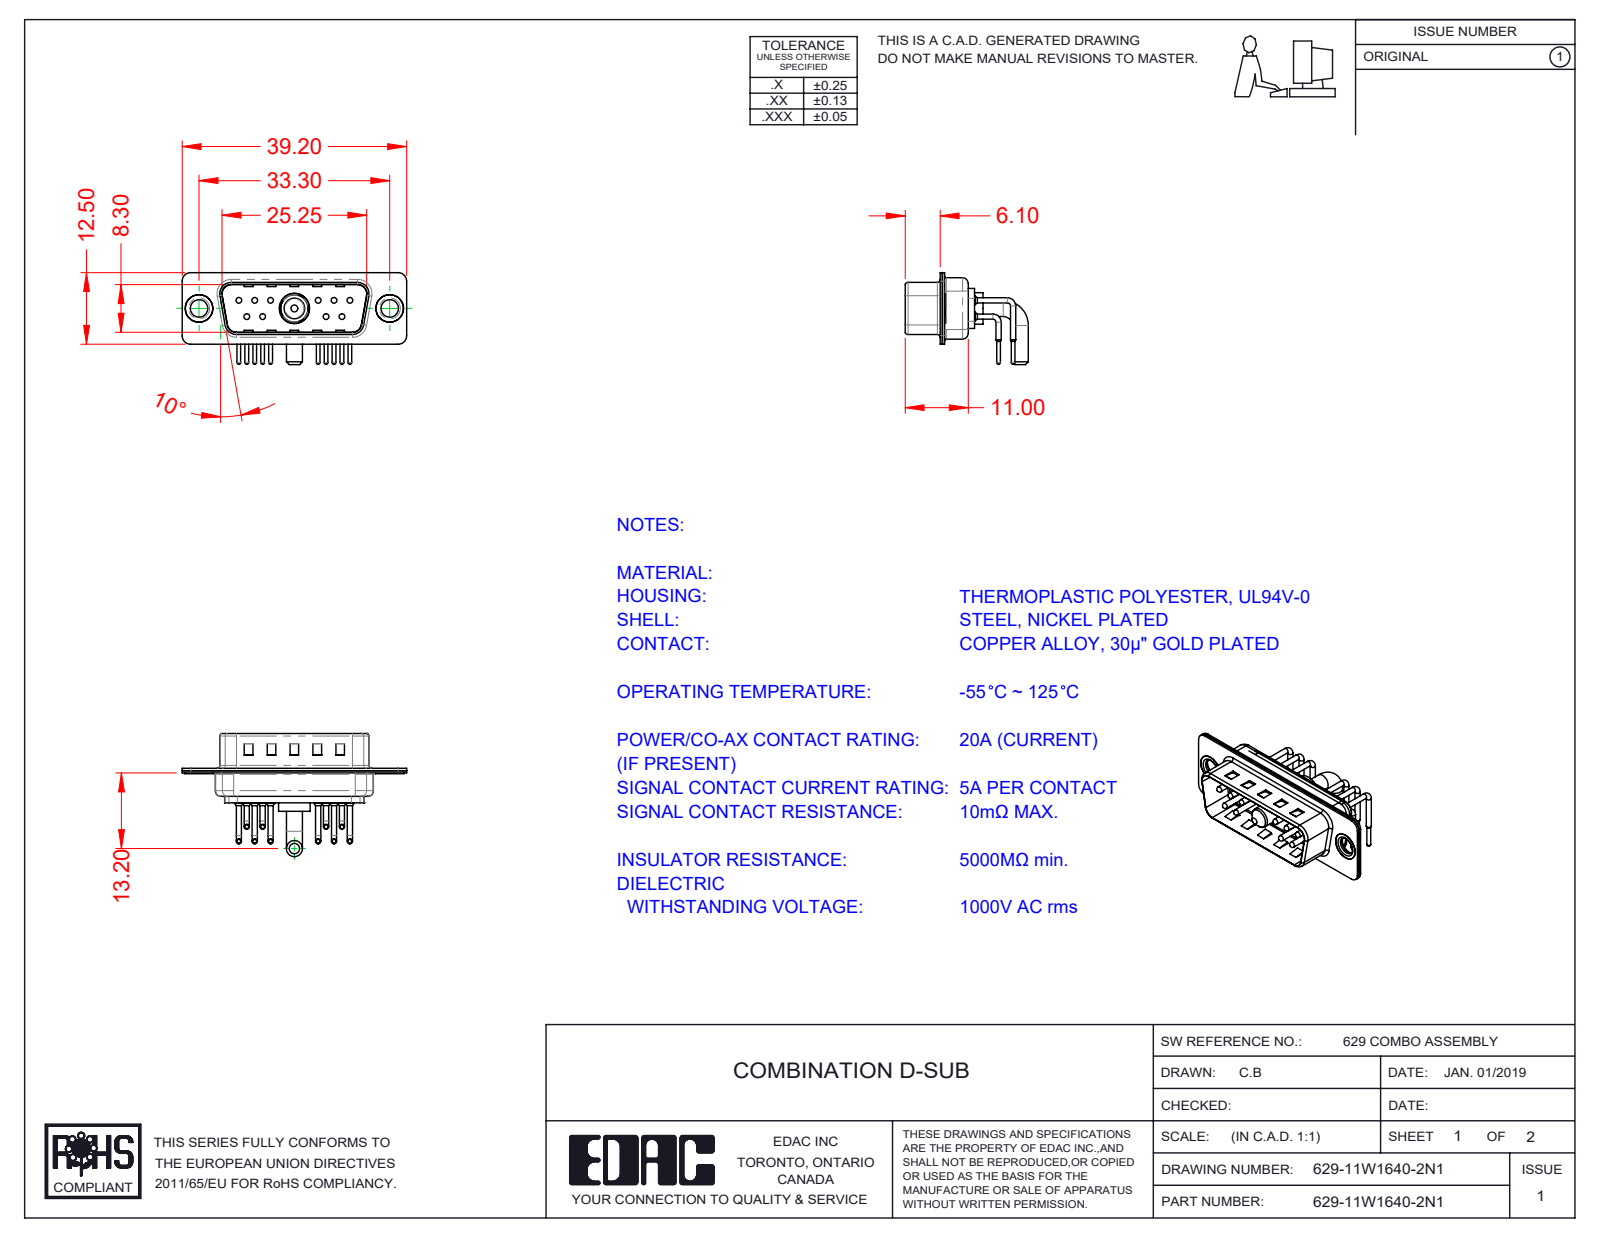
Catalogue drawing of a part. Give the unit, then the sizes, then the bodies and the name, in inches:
Units: inches
Overall size (bounding box): 1.543 × 0.846 × 0.632
Round holes (diameter × count): ⌀0.03 ×10, ⌀0.063 ×10, ⌀0.079 ×10, ⌀0.12 ×2, ⌀0.157 ×2, ⌀0.189 ×2, ⌀0.191 ×1, ⌀0.209 ×1
Round bosses / shafts (diameter × count): ⌀0.035 ×20, ⌀0.059 ×10, ⌀0.039 ×10, ⌀0.026 ×10, ⌀0.197 ×2, ⌀0.193 ×2, ⌀0.14 ×2, ⌀0.11 ×2
Partial cylindrical surfaces — rounded edges, fillets, slot ends (radius × count): R0.059 ×16, R0.079 ×12, R0.04 ×10, R0.02 ×8, R0.063 ×8, R0.039 ×7, R0.01 ×4, R0.024 ×4
Main face-to-face distances: 0.016, 0.031, 0.374, 0.358, 0.343, 0.39, 0.03, 0.22, 0.047, 0.014
Hole centre spacings: 0.124, 0.109, 0.545, 0.436, 0.654, 0.198, 0.198, 0.218
Volume: 0.121 in³ · Surface area: 7.886 in²
Bodies: 17 solids, 1470 faces (798 planar, 502 cylindrical, 170 other)
Part name (STEP PRODUCT): Power Pin_20A RA; 629Combo Shell Rear_15 Contacts; 629Combo Thru Hole Rivet; 629Combo Contact Row 2 (+4 more)
STEP written by: SolidWorks 2020 (CONFIG_CONTROL_DESIGN)
